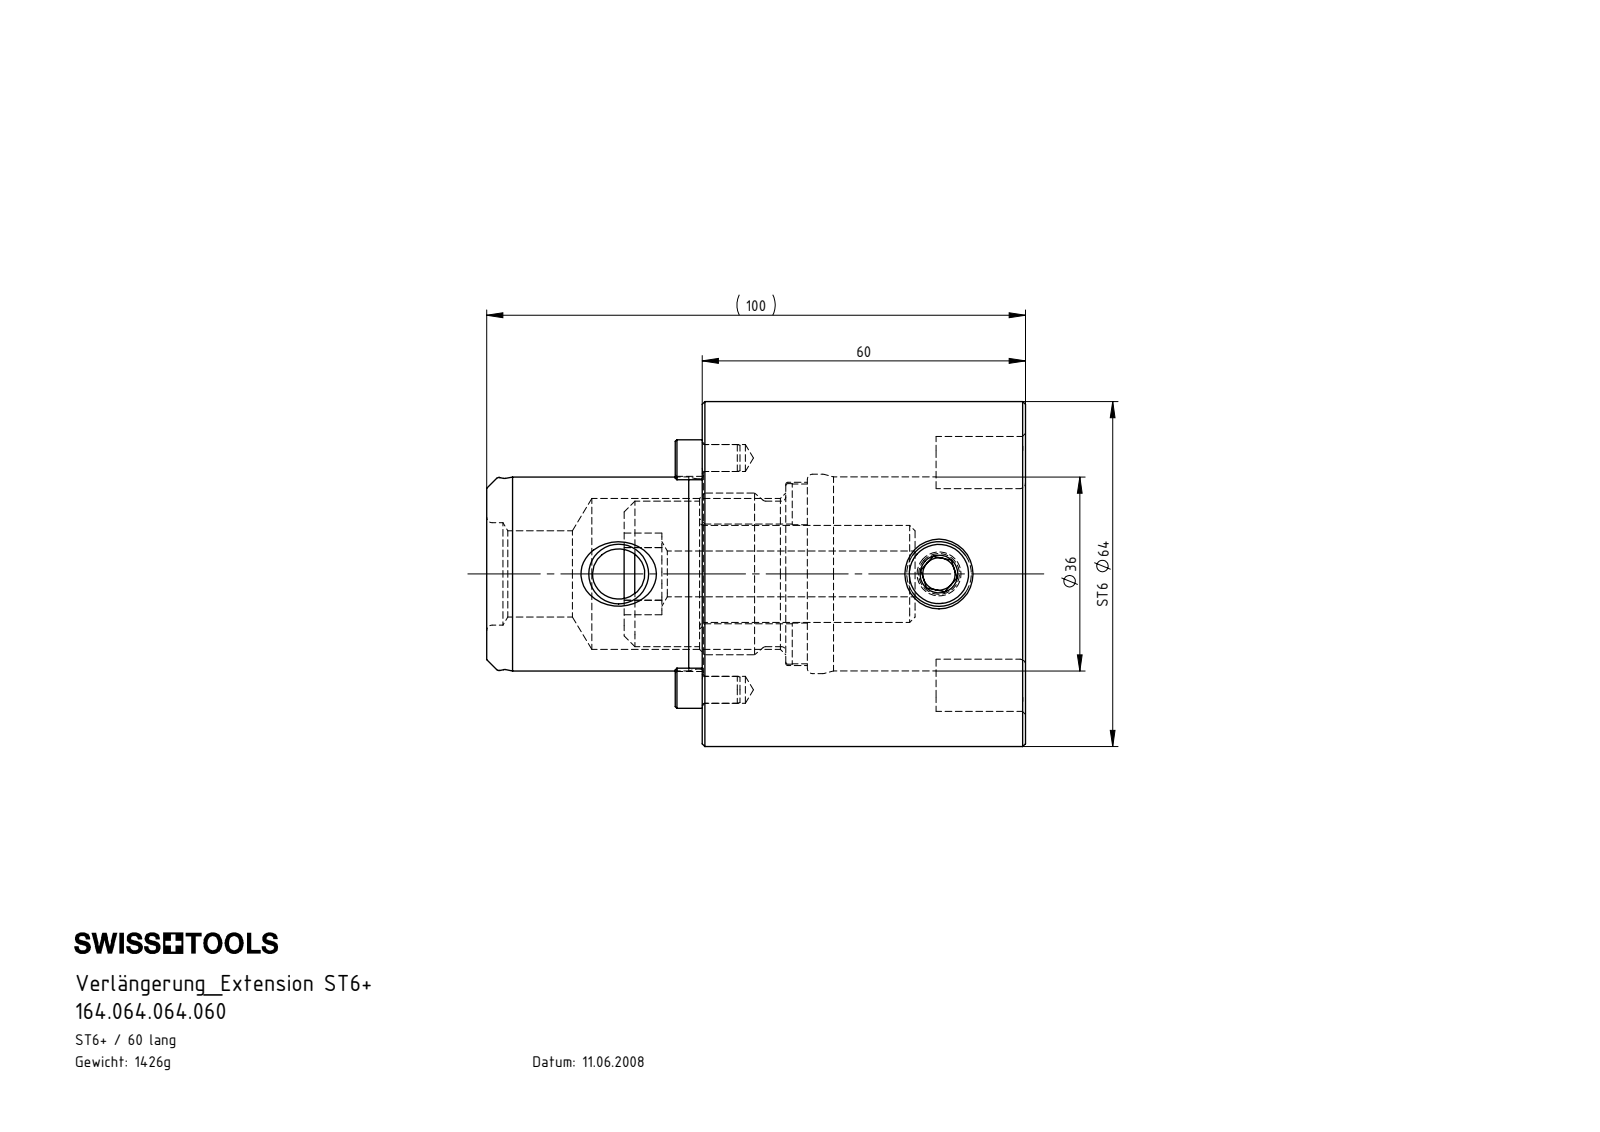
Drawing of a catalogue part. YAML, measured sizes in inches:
part_name: "ST6-ST6.K01.060_B; ST6-ER1.001.018_A; ST6-ER3.K01.040_A_PreviewCfg; ST6-ER4.001.020_A (+2 more)"
step_written_by: "SolidWorks 2015 (CONFIG_CONTROL_DESIGN)"
units: inches
bodies: {solids: 6, faces: 231, planar: 46, cylindrical: 76, other: 109}
overall_size: [3.937, 2.52, 2.52]
volume: 11.09
surface_area: 68.27
round_holes:
  - {diameter: 0.197, count: 2}
  - {diameter: 0.335, count: 1}
  - {diameter: 0.433, count: 1}
  - {diameter: 0.63, count: 1}
  - {diameter: 0.728, count: 1}
  - {diameter: 0.748, count: 1}
  - {diameter: 1.102, count: 1}
  - {diameter: 1.339, count: 1}
  - {diameter: 1.417, count: 1}
  - {diameter: 1.457, count: 1}
round_bosses_or_shafts:
  - {diameter: 2.52, count: 1}
  - {diameter: 1.409, count: 1}
  - {diameter: 1.39, count: 1}
  - {diameter: 1.319, count: 1}
  - {diameter: 1.181, count: 1}
  - {diameter: 1.063, count: 1}
  - {diameter: 0.709, count: 1}
  - {diameter: 0.472, count: 1}
partial_cylinders:
  - {radius: 0.063, count: 6}
  - {radius: 0.177, count: 6}
  - {radius: 0.02, count: 4}
  - {radius: 0.205, count: 2}
  - {radius: 0.215, count: 2}
  - {radius: 0.711, count: 2}
face_to_face_distances: [2.362, 0.787, 0.768, 1.594, 1.555, 1.575, 0.02, 2.382, 1.752, 2.343]
hole_center_spacings: [0.846, 1.693]
